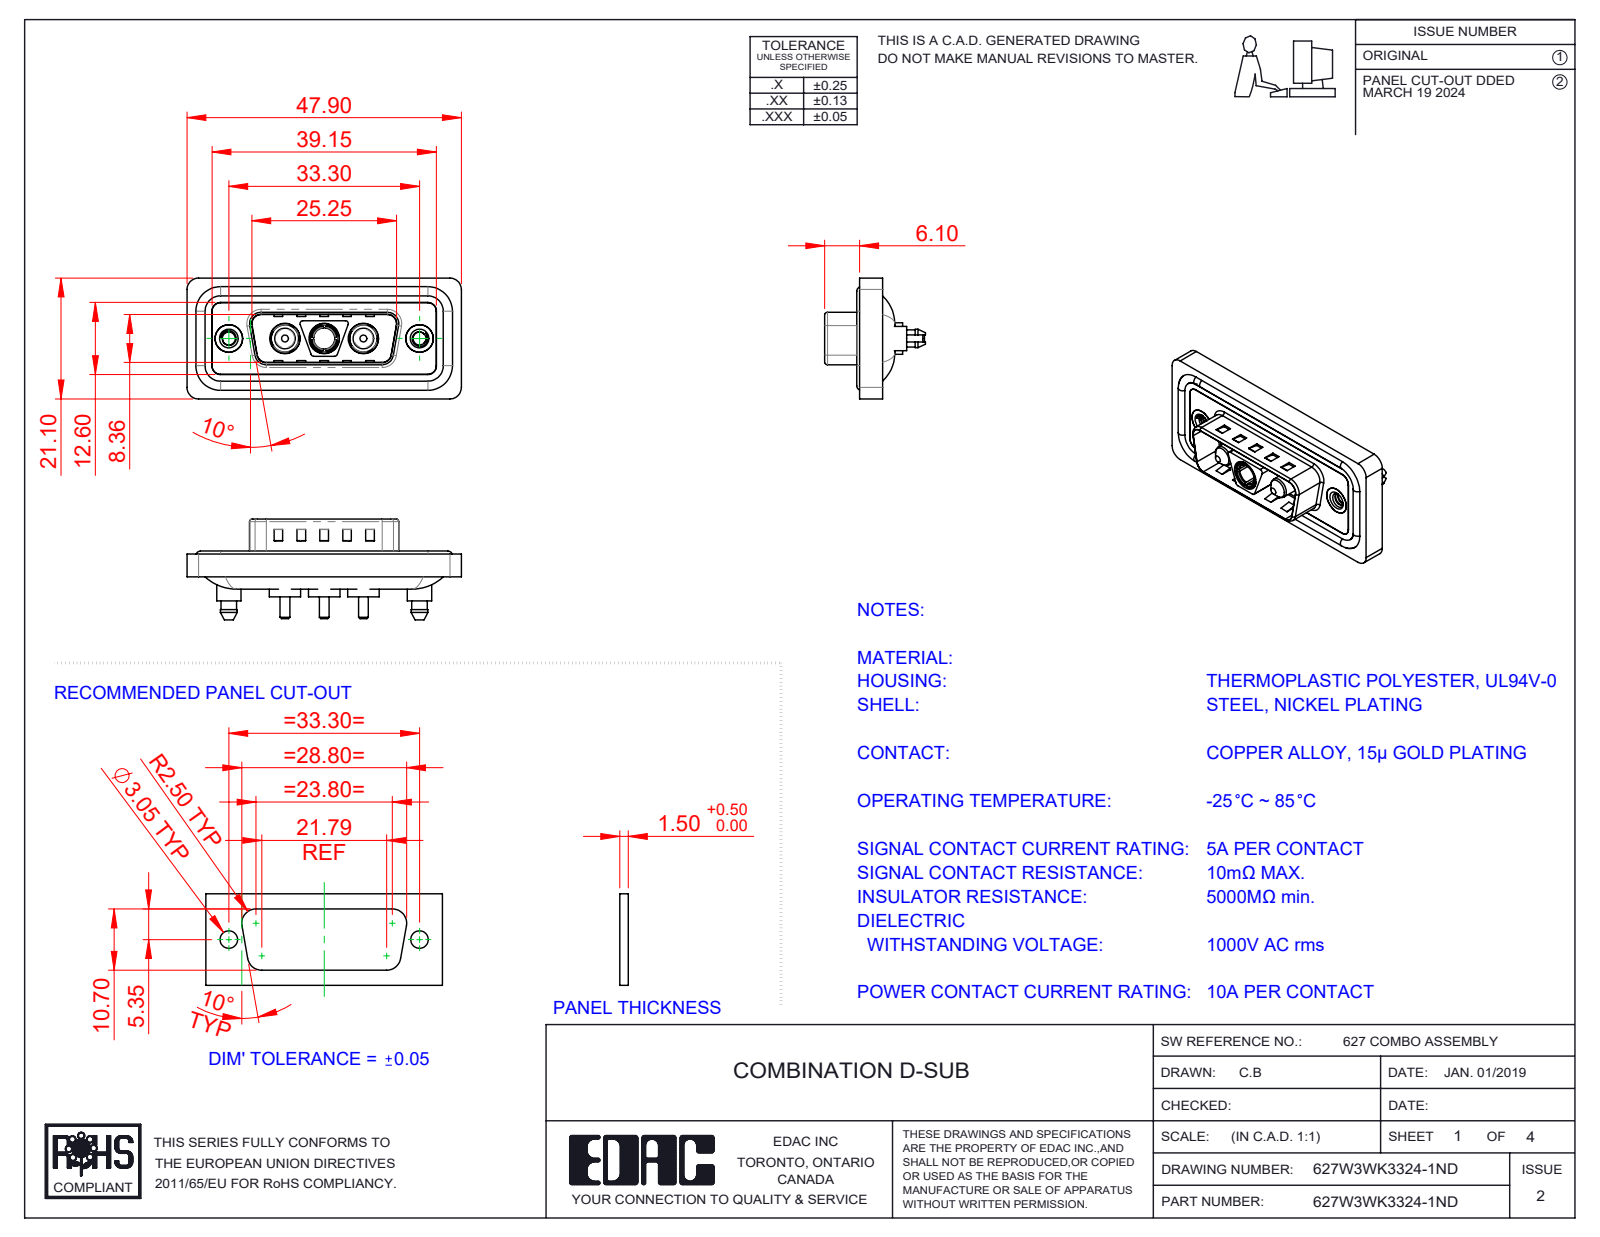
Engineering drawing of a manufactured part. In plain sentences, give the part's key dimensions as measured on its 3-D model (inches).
The part is named "627Combo Threaded Boardlock_5; 627Combo Threaded Boardlock_D; 627W3WK3324-1ND; 627Combo Waterproof Housing_15 Contacts (+5 more)". Its 3-D file was written by "SolidWorks 2023 (CONFIG_CONTROL_DESIGN)". It is 13 solids with 667 faces: 247 planar, 290 cylindrical and 130 other. Overall it measures 1.886 by 0.831 by 0.693 inches. Its volume is 0.353 cubic inches and its surface area 14.61 square inches. Round holes: 3 of diameter 0.191, 3 of diameter 0.209, 2 of diameter 0.089, 2 of diameter 0.157, 2 of diameter 0.189, 2 of diameter 0.197, 1 of diameter 0.146. Round bosses or shafts: 4 of diameter 0.063, 3 of diameter 0.217, 3 of diameter 0.205, 3 of diameter 0.187, 3 of diameter 0.148, 3 of diameter 0.067, 2 of diameter 0.213, 2 of diameter 0.193. Partial cylindrical surfaces (rounded edges, fillets, slot ends): 28 of radius 0.059, 20 of radius 0.079, 12 of radius 0.02, 10 of radius 0.063, 4 of radius 0.01, 4 of radius 0.024, 4 of radius 0.026, 4 of radius 0.035. The main face-to-face distances are 0.016, 0.059, 0.043, 0.02, 0.063, 0.122, 0.114, 0.157, 0.028, 0.032. The hole center spacings are 0.27, 0.386, 0.656, 0.925, 0.539, 1.311.
